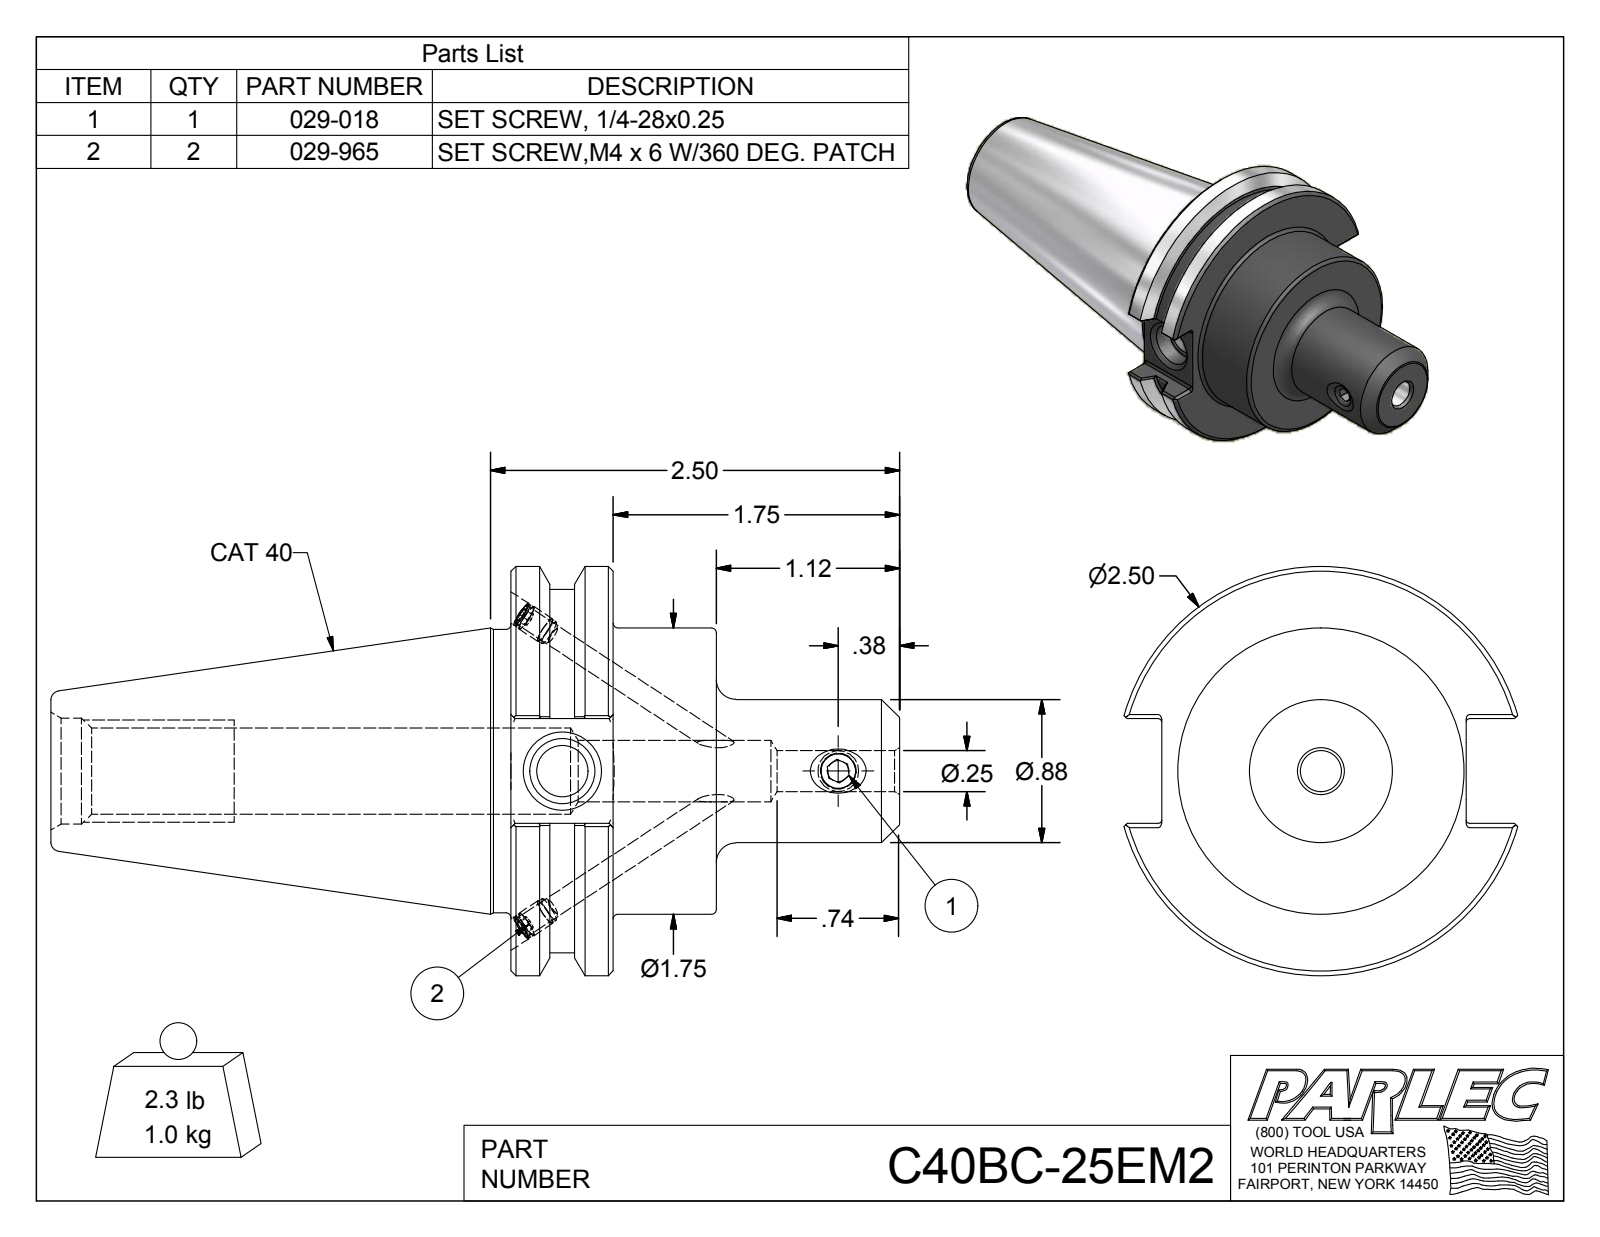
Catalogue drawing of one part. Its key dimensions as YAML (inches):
part_name: "C40BC-25EM2; C40BC-25EM2-1; 029-018; 029-965"
step_written_by: "Autodesk Inventor 2012 (AUTOMOTIVE_DESIGN)"
units: inches
bodies: {solids: 4, faces: 143, planar: 63, cylindrical: 39, other: 41}
overall_size: [5.187, 2.5, 2.406]
volume: 8.15
surface_area: 41.22
round_holes:
  - {diameter: 0.13, count: 2}
  - {diameter: 0.161, count: 2}
  - {diameter: 0.211, count: 1}
  - {diameter: 0.25, count: 1}
  - {diameter: 0.315, count: 1}
  - {diameter: 0.375, count: 1}
  - {diameter: 0.399, count: 1}
  - {diameter: 0.527, count: 1}
  - {diameter: 0.648, count: 1}
round_bosses_or_shafts:
  - {diameter: 0.165, count: 2}
  - {diameter: 0.157, count: 2}
  - {diameter: 2.5, count: 1}
  - {diameter: 2.219, count: 1}
  - {diameter: 1.75, count: 1}
  - {diameter: 1.73, count: 1}
  - {diameter: 0.875, count: 1}
  - {diameter: 0.25, count: 1}
partial_cylinders:
  - {radius: 0.02, count: 12}
face_to_face_distances: [0.625, 1.255, 0.63, 2.375, 1.75, 1.12, 0.64, 1.86, 2.812, 3.437]
hole_center_spacings: [1.685]
